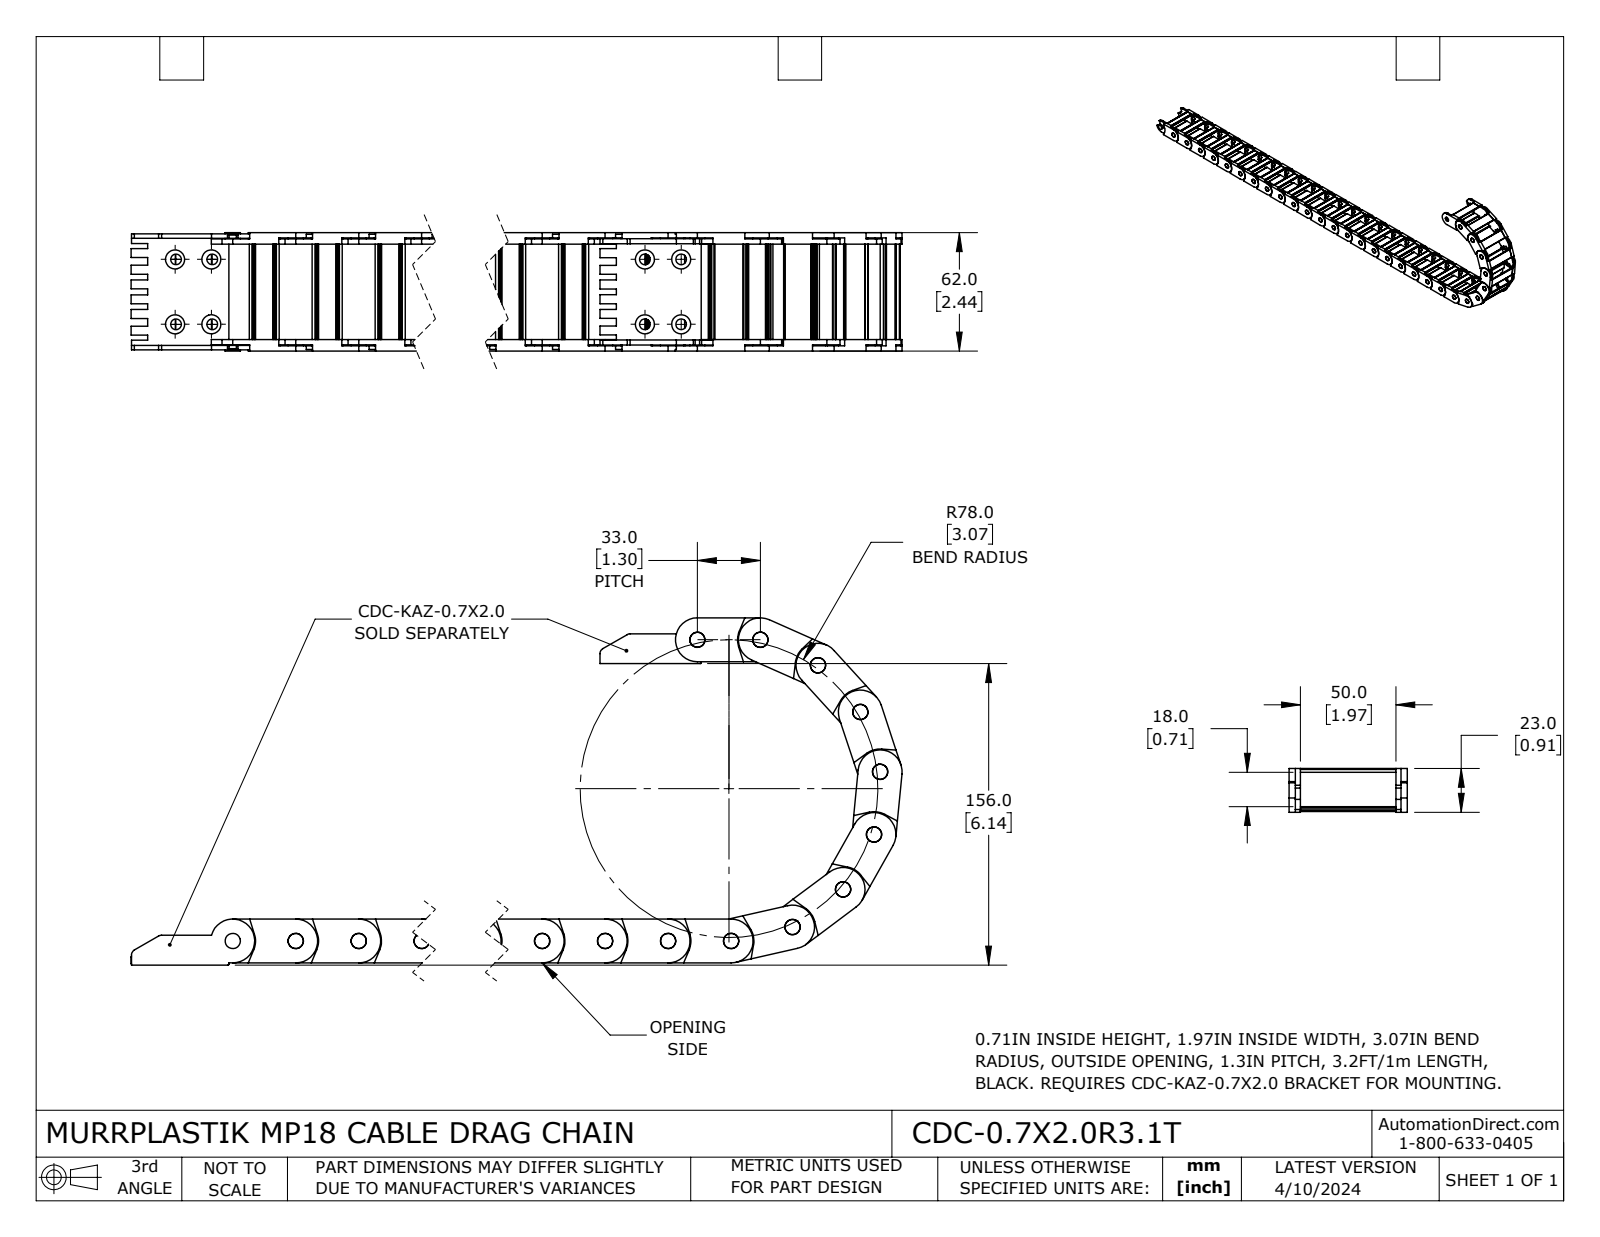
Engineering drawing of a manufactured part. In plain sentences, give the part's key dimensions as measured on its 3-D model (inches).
The part is named "CDC-0.7X2.0R3.1T". Its 3-D file was written by "SolidWorks 2023 (CONFIG_CONTROL_DESIGN)". It is 30 solids with 2280 faces: 1110 planar, 1170 cylindrical and 0 other. Overall it measures 32.549 by 7.115 by 2.441 inches. Its volume is 18.99 cubic inches and its surface area 406.4 square inches. Round holes: 30 of diameter 0.315. Round bosses or shafts: 1 of diameter 0.315. Partial cylindrical surfaces (rounded edges, fillets, slot ends): 120 of radius 0.02, 120 of radius 0.059, 60 of radius 0.008, 60 of radius 0.012, 31 of radius 0.453, 31 of radius 0.47, 30 of radius 0.197, 30 of radius 0.215. The main face-to-face distances are 2.205, 0.106, 0.13, 0.236, 2.441, 2.311, 2.075, 2.098, 2.335, 0.024. The hole center spacings are 1.299, 2.598, 3.898, 5.197, 6.496, 7.795, 9.094, 10.394.
